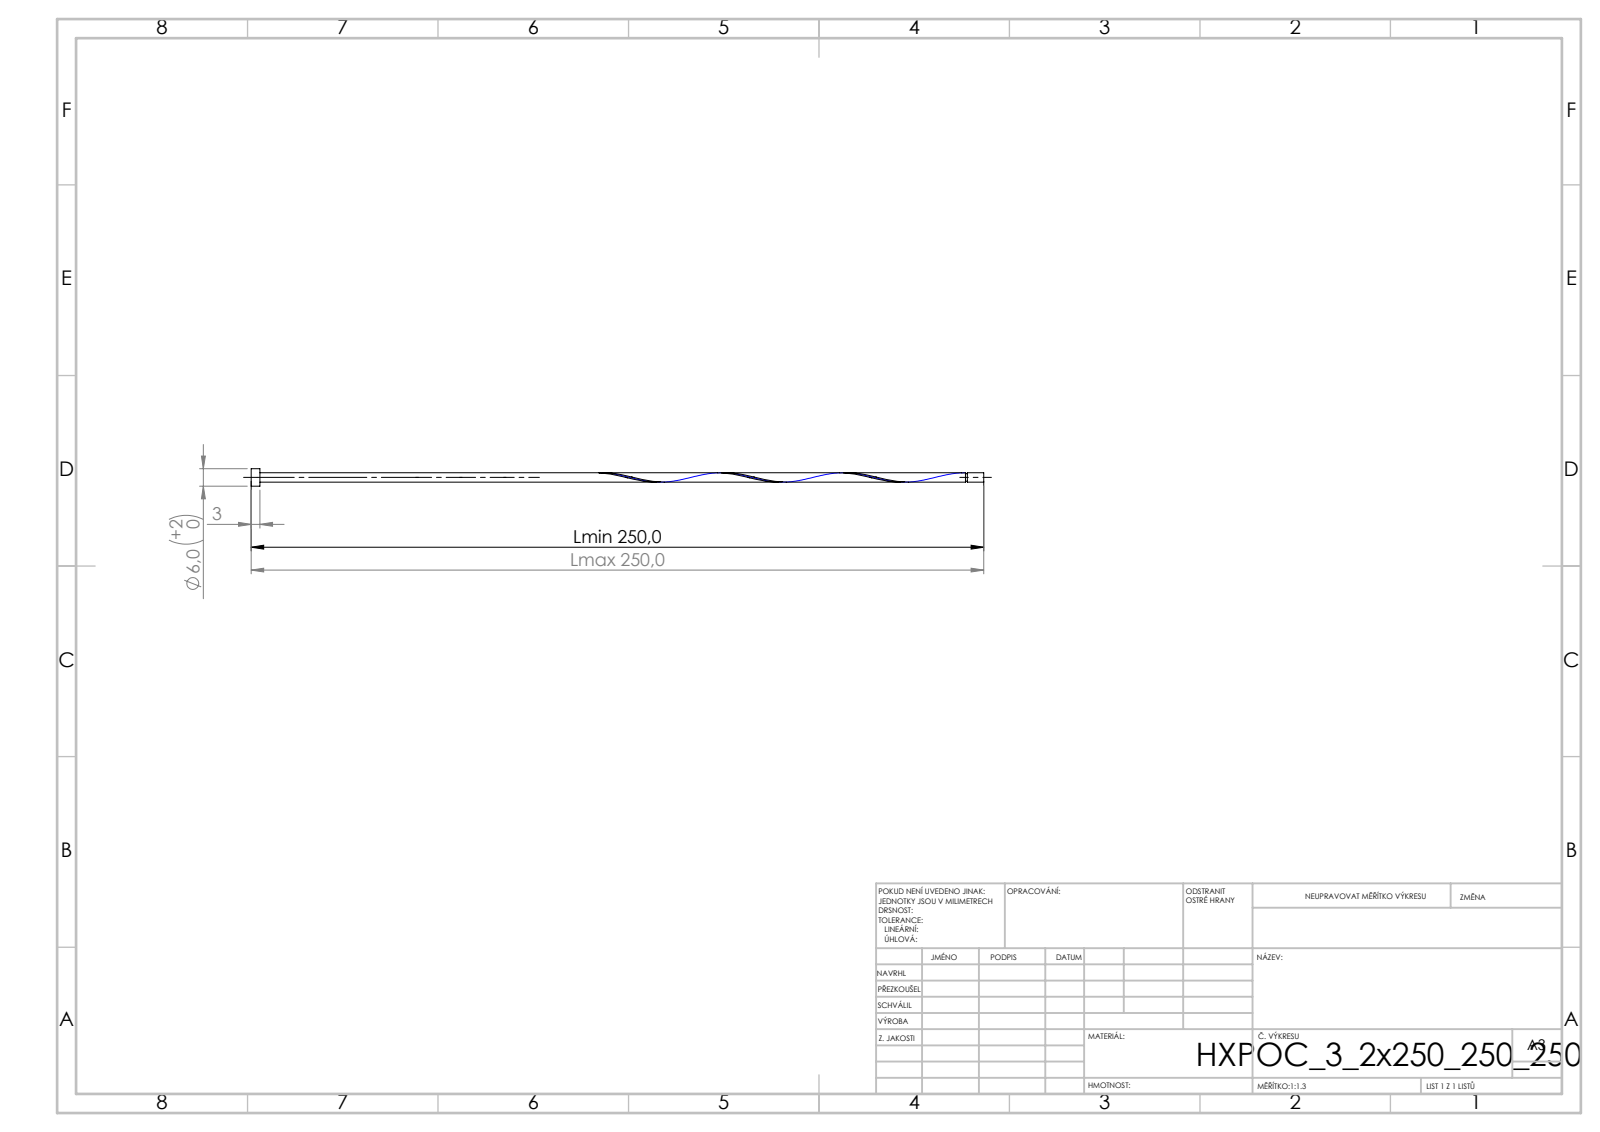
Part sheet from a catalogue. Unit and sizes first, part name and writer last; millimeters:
Units: millimetres
Overall size (bounding box): 250 × 6 × 6
Round bosses / shafts (diameter × count): ⌀6 ×1, ⌀3.2 ×1, ⌀2.56 ×1
Main face-to-face distances: 3, 250, 247, 244.41, 241.41, 5.59, 243.77, 240.77, 0.64, 6.23
Volume: 2 497 mm³ · Surface area: 3 478 mm²
Bodies: 1 solid, 16 faces (6 planar, 9 cylindrical, 1 other)
STEP written by: SolidWorks 2019 (CONFIG_CONTROL_DESIGN)
